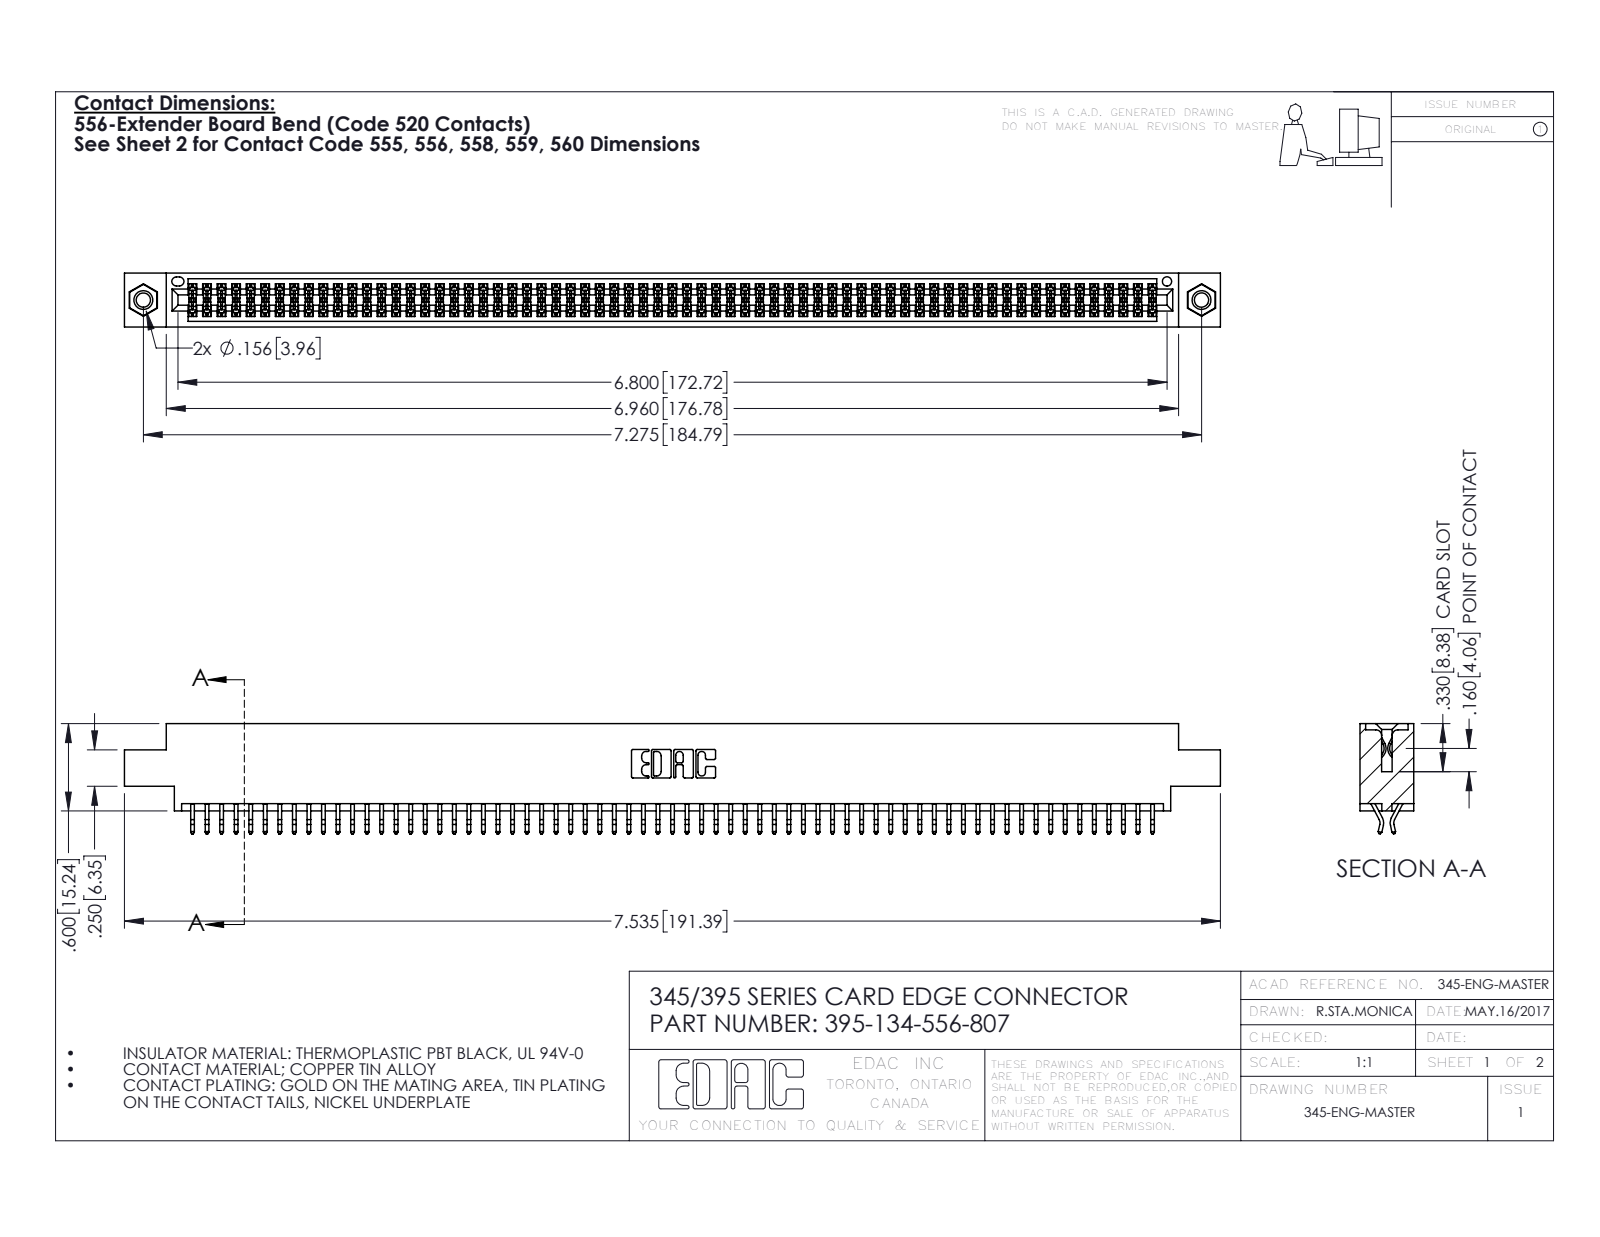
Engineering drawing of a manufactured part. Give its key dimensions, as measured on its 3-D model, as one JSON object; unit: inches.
{"part_name": "345-250-001_345-250-005-103; 345 Part_0.170 Offset - 0.156 Dia-TI; 395-134-556-807; 345-292-001_556 Tail", "step_written_by": "SolidWorks 2016 (CONFIG_CONTROL_DESIGN)", "units": "inches", "bodies": {"solids": 137, "faces": 7694, "planar": 5074, "cylindrical": 2604, "other": 16}, "overall_size": [7.535, 0.757, 0.37], "volume_in3": 1.141, "surface_area_in2": 43.66, "round_holes": [[0.098, 2], [0.125, 2], [0.156, 2], [0.064, 1]], "round_bosses_or_shafts": [[0.155, 2]], "partial_cylinders_radius": [[0.006, 201], [0.01, 22], [0.007, 6], [0.031, 6], [0.026, 3], [0.01, 2], [0.014, 2], [0.019, 2]], "face_to_face_distances": [0.072, 0.298, 0.37, 0.2, 0.025, 0.098, 0.272, 0.225, 0.175, 0.149], "hole_center_spacings": [0.27, 7.039, 7.275]}
